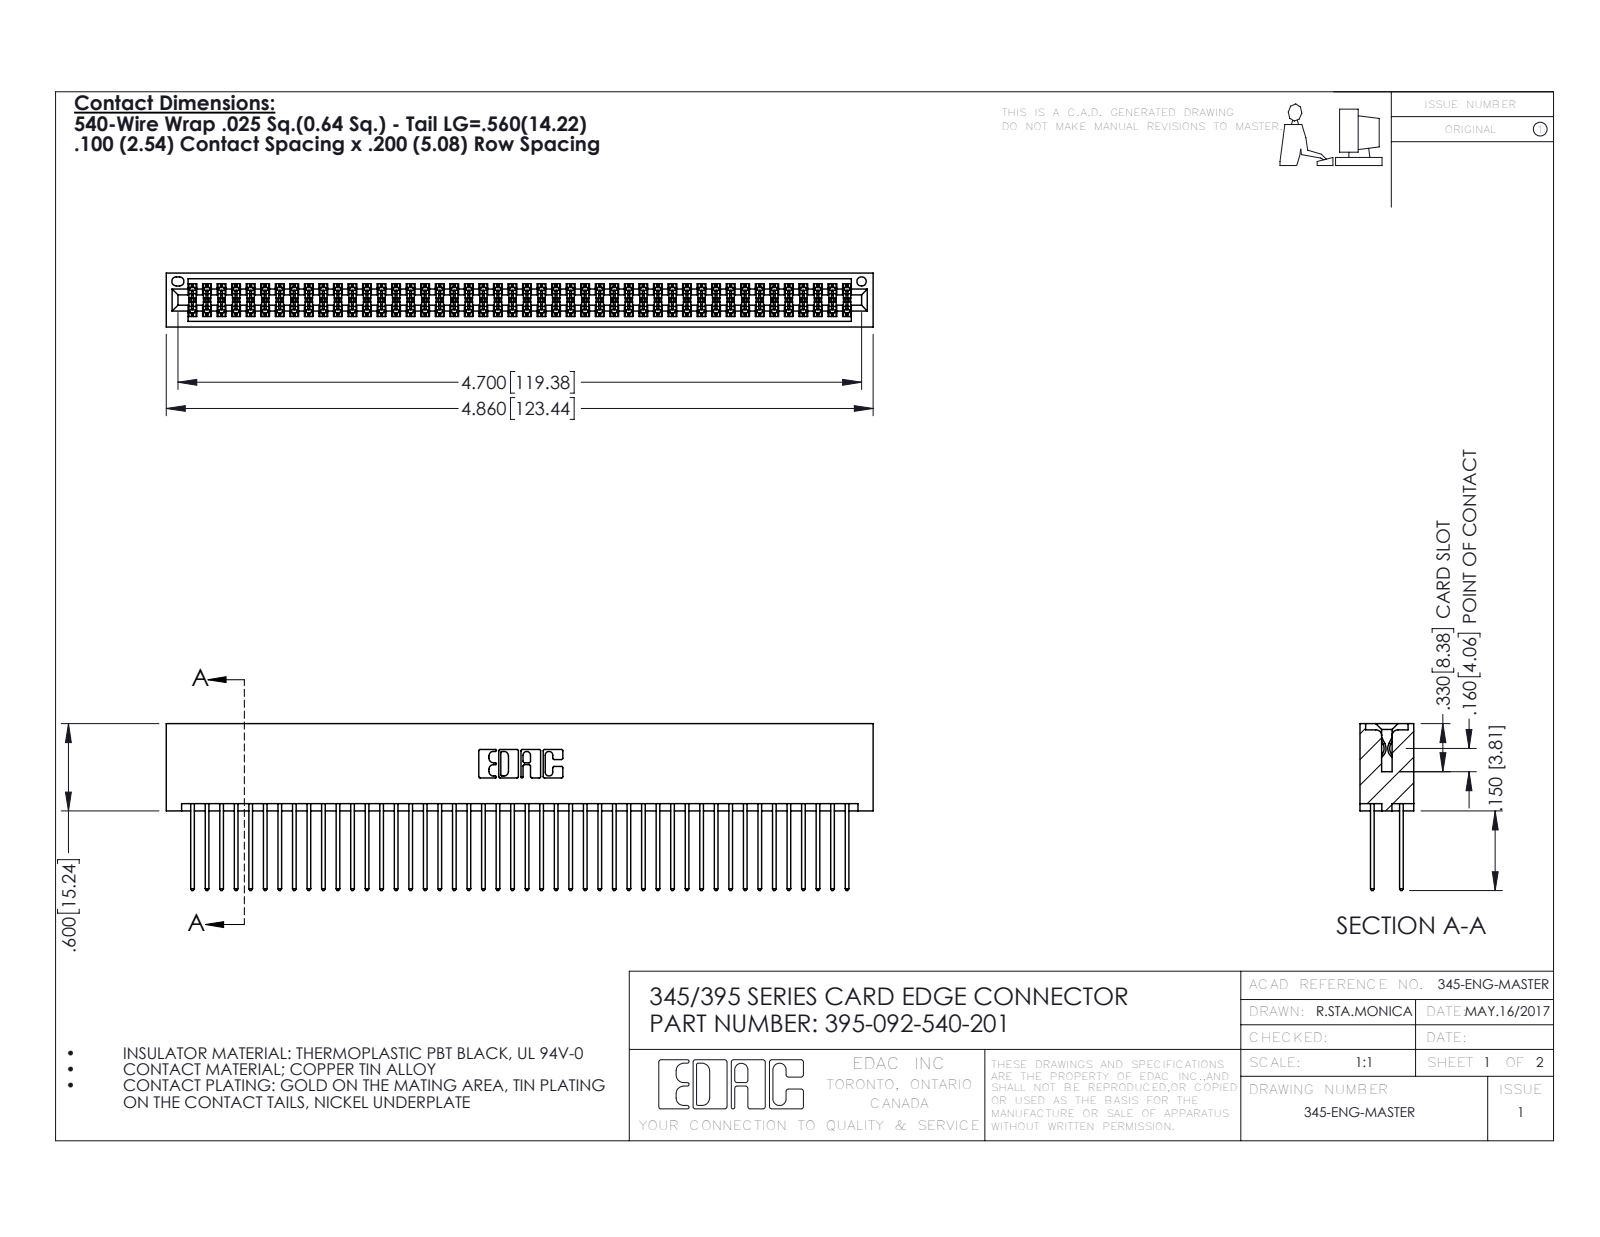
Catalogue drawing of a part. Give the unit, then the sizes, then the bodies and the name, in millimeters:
Units: millimetres
Overall size (bounding box): 123.4 × 29.1 × 9.4
Round holes (diameter × count): ⌀1.6 ×1
Partial cylindrical surfaces — rounded edges, fillets, slot ends (radius × count): R0.2 ×138, R0.3 ×92, R0.3 ×22, R0.2 ×6, R0.8 ×6, R0.7 ×3, R0.4 ×2, R0.5 ×2
Main face-to-face distances: 7.6, 1.8, 5.1, 2.5, 6.9, 0.6, 5.7, 9.4, 4.4, 3.8
Volume: 13 000 mm³ · Surface area: 21 210 mm²
Bodies: 93 solids, 4718 faces (3112 planar, 1606 cylindrical, 0 other)
Part name (STEP PRODUCT): 345 Part_No Mounting Lugs; 395-092-540-201; 345-292-001_345-293-140
STEP written by: SolidWorks 2016 (CONFIG_CONTROL_DESIGN)
